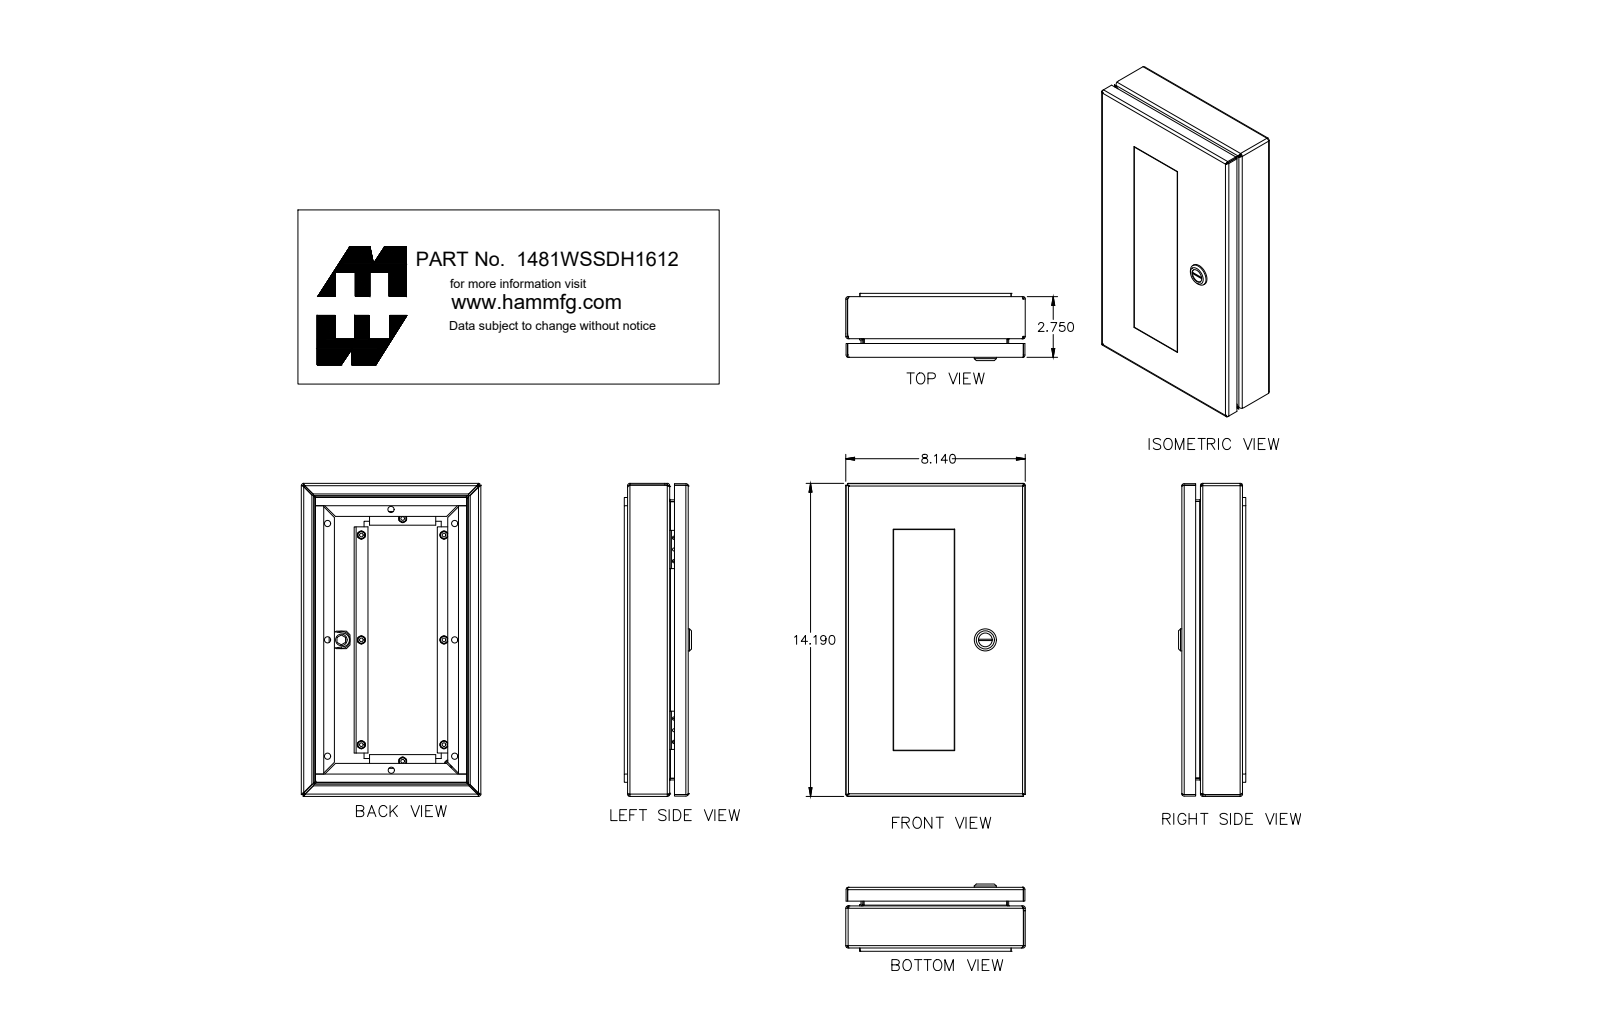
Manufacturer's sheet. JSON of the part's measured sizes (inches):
{"part_name": "1481WSSDH1612_Default", "step_written_by": "SolidWorks 2019 (CONFIG_CONTROL_DESIGN)", "units": "inches", "bodies": {"solids": 36, "faces": 875, "planar": 475, "cylindrical": 252, "other": 148}, "overall_size": [14.19, 8.14, 2.91], "volume_in3": 32.55, "surface_area_in2": 782.4, "round_holes": [[0.281, 8], [0.13, 6], [0.136, 2], [0.197, 1], [0.24, 1], [0.242, 1], [0.387, 1], [0.5, 1], [0.63, 1], [0.768, 1]], "round_bosses_or_shafts": [[0.226, 8], [0.164, 8], [0.368, 6], [1.1, 1], [0.785, 1], [0.625, 1], [0.525, 1], [0.477, 1]], "partial_cylinders_radius": [[0.036, 28], [0.108, 28], [0.101, 16], [0.016, 4], [0.088, 4], [0.125, 2], [0.021, 1], [0.029, 1]], "face_to_face_distances": [0.072, 0.25, 2.578, 0.178, 0.842, 1.736, 8.068, 2.328, 0.592, 2.678], "hole_center_spacings": [2.951, 11.545, 5.764, 3.75, 4.75, 5.273, 5.273, 6.052]}
